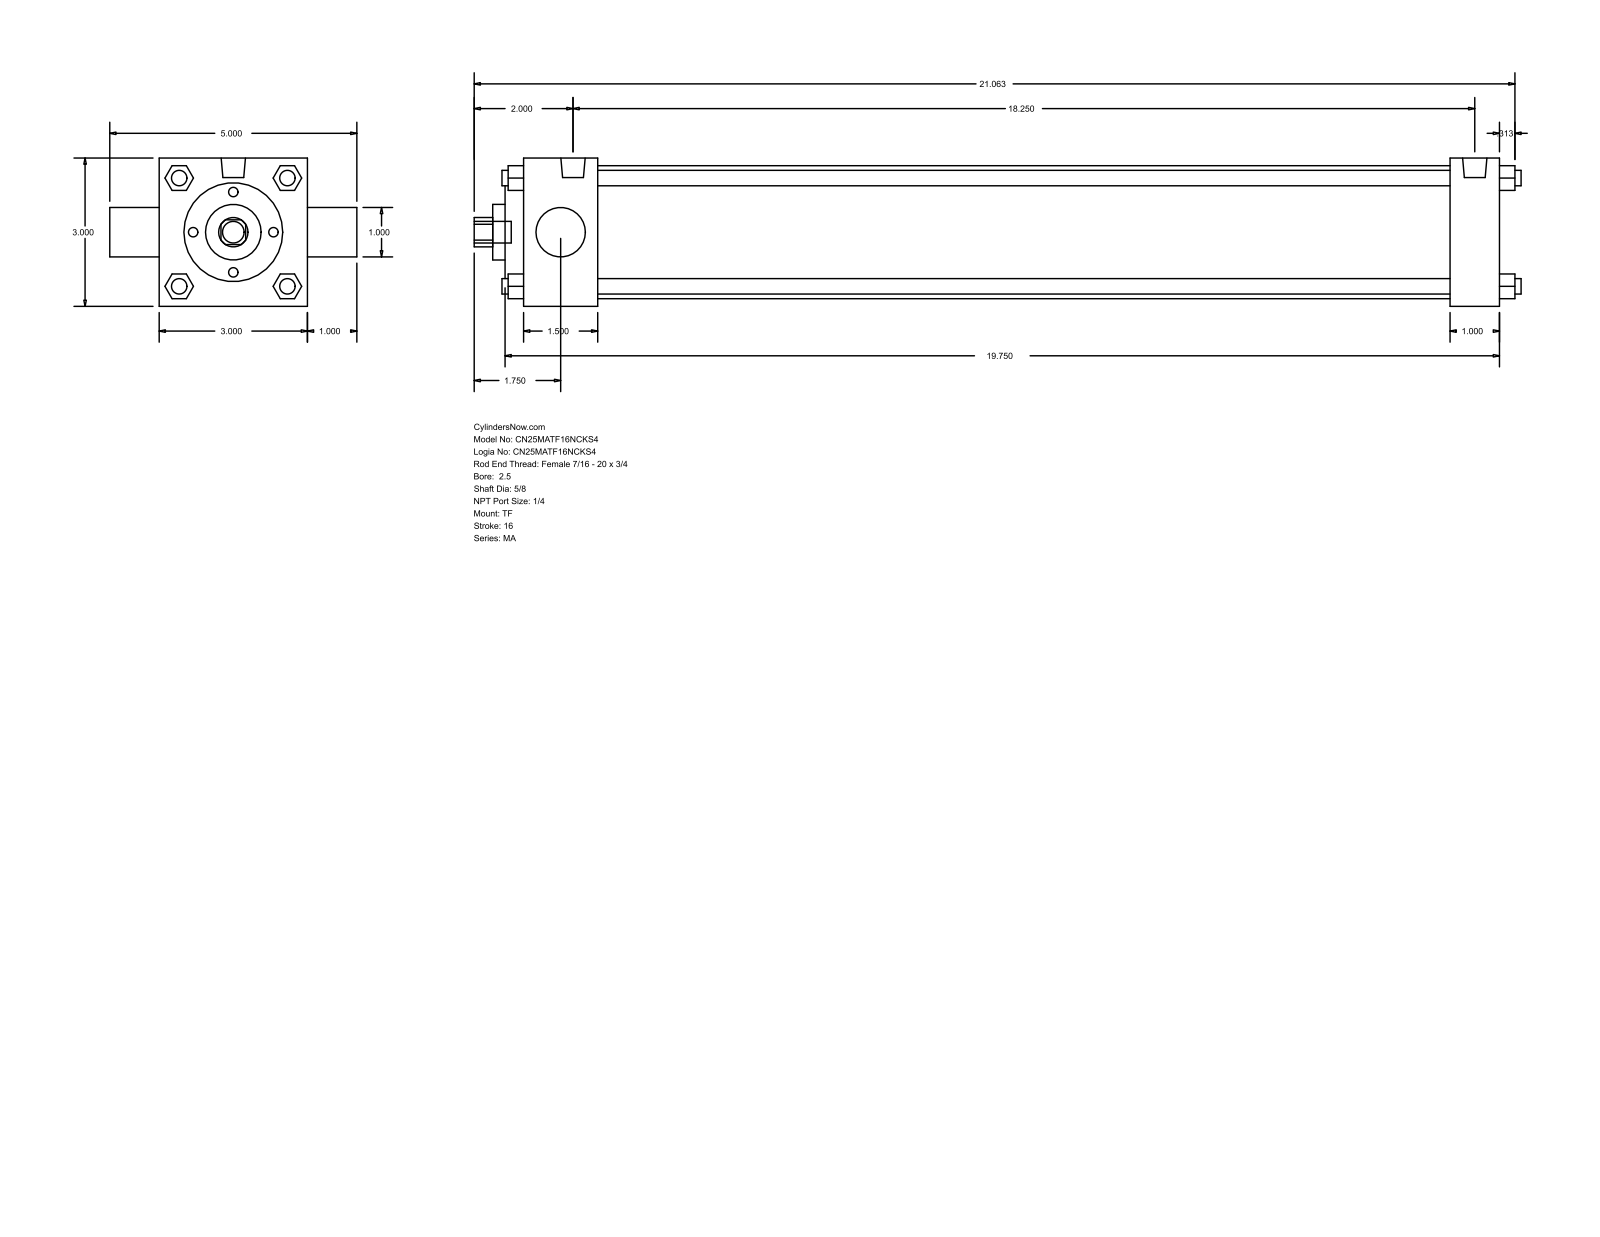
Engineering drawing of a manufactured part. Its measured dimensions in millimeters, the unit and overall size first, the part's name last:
Units: millimetres
Overall size (bounding box): 538.16 × 127 × 76.2
Round holes (diameter × count): ⌀15.88 ×1, ⌀25.4 ×1, ⌀28.57 ×1, ⌀50.8 ×1, ⌀68.33 ×1
Round bosses / shafts (diameter × count): ⌀7.94 ×7, ⌀12.49 ×2, ⌀11.11 ×1
Partial cylindrical surfaces — rounded edges, fillets, slot ends (radius × count): R7.54 ×1
Main face-to-face distances: 76.2, 501.65, 25.4, 38.1, 476.25, 438.15, 463.55, 12.7, 9.52, 47.62
Bodies: 0 solids, 122 faces (93 planar, 29 cylindrical, 0 other)
Part name (STEP PRODUCT): MA_TF__0250_0.625
STEP written by: GSSL Pune (CONFIG_CONTROL_DESIGN)
